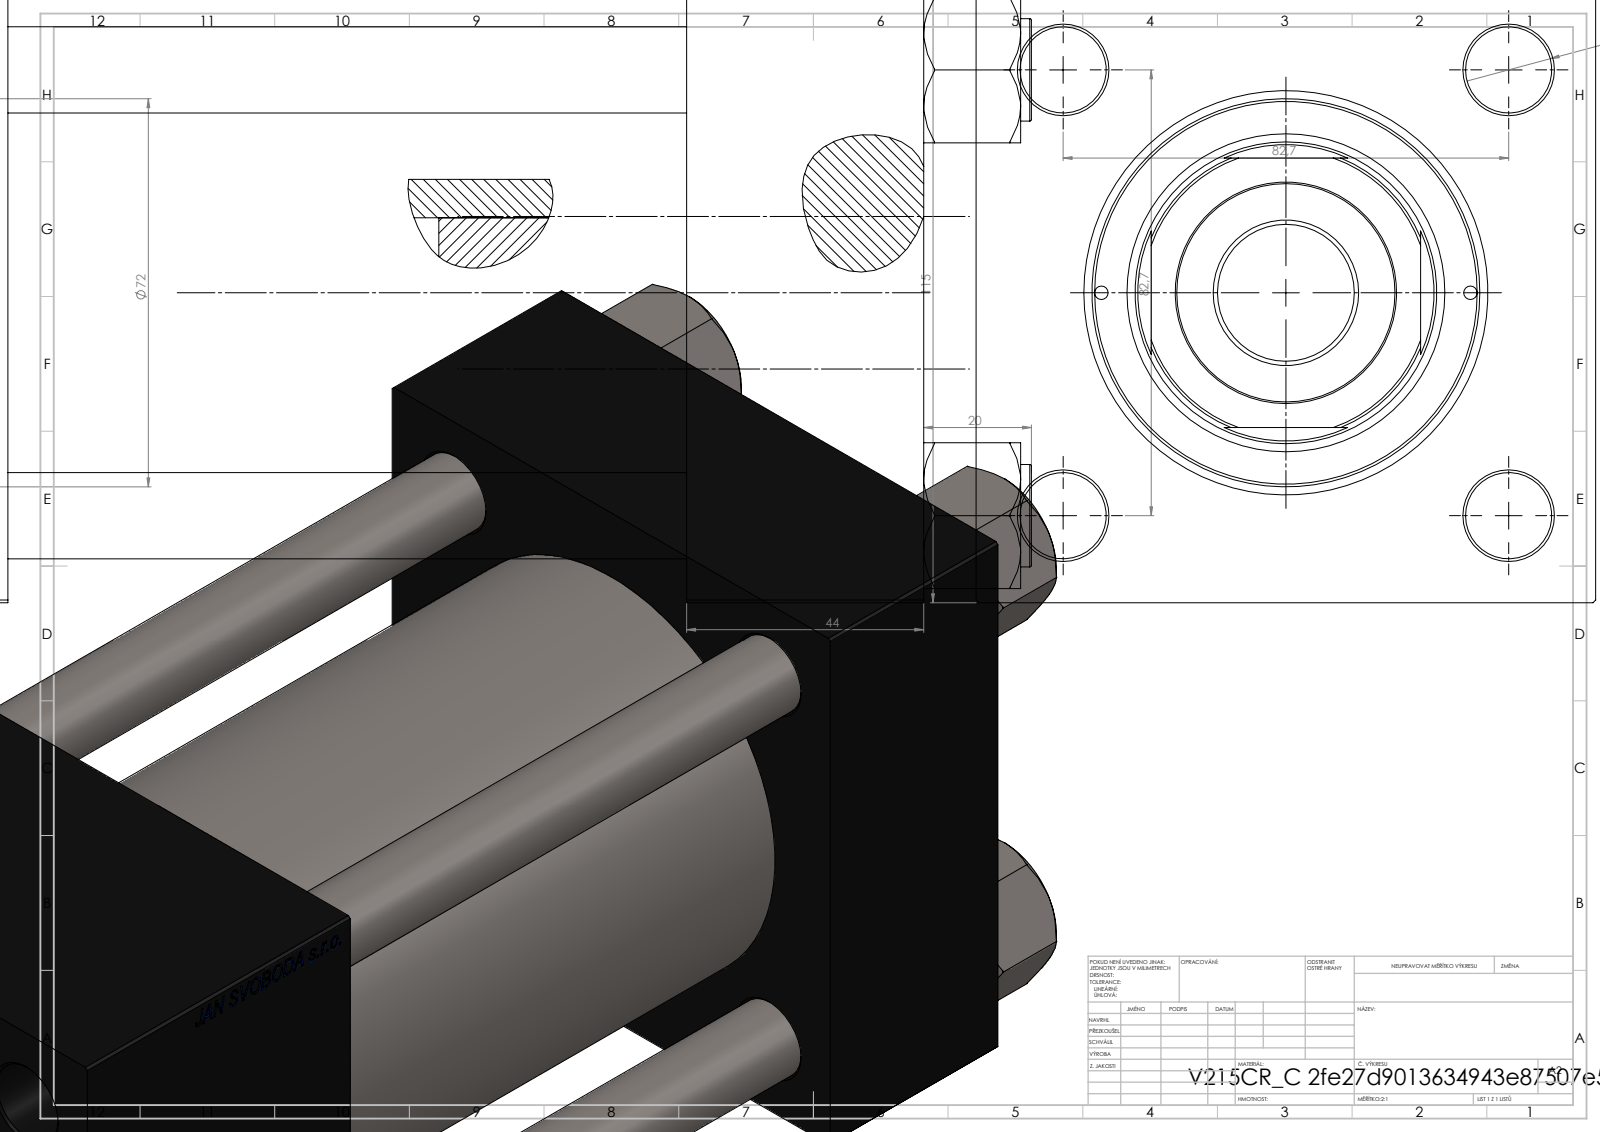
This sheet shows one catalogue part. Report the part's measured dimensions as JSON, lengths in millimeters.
{"part_name": "ROD_END_E; V215CR_VCP_C; V215CR_C_Body; NUT_M5_C (+2 more)", "step_written_by": "SolidWorks 2019 (CONFIG_CONTROL_DESIGN)", "units": "millimeters", "bodies": {"solids": 12, "faces": 1214, "planar": 579, "cylindrical": 93, "other": 542}, "overall_size": [326, 115, 115], "volume_mm3": 2125000, "surface_area_mm2": 338614, "round_holes": [[16, 4], [2.5, 2], [7, 2], [26.44, 2], [35, 2], [40.5, 1], [56, 1], [59, 1], [61, 1], [72, 1], [80, 1]], "round_bosses_or_shafts": [[19, 4], [86, 1], [27, 1], [25, 1]], "partial_cylinders_radius": [[27, 1]], "face_to_face_distances": [115, 44, 170, 126, 239, 195, 69, 210.3, 166.3, 40.3], "hole_center_spacings": [41.96, 58.48, 82.7, 86.17, 34.25, 116.96, 68.5]}
